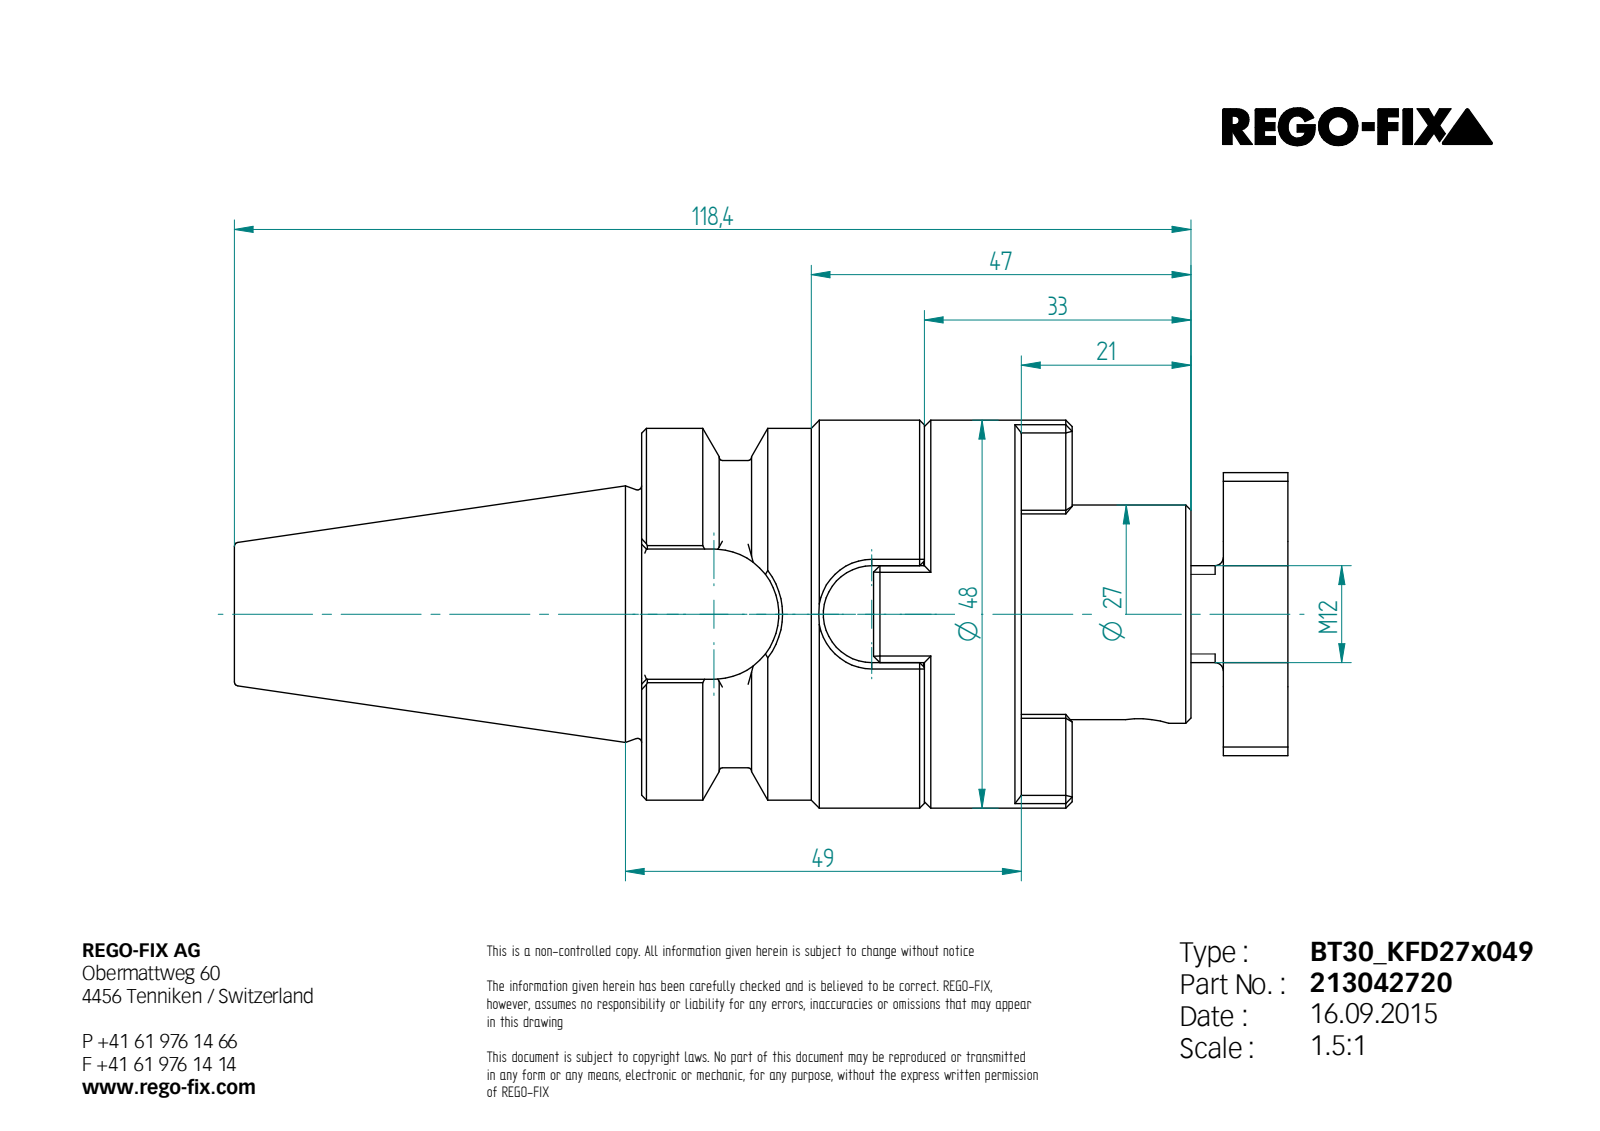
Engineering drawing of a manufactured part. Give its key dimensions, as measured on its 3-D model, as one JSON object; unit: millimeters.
{"step_written_by": "Unknown (AUTOMOTIVE_DESIGN)", "units": "millimeters", "bodies": {"solids": 3, "faces": 214, "planar": 119, "cylindrical": 39, "other": 56}, "overall_size": [130.4, 48, 48], "volume_mm3": 110950, "surface_area_mm2": 28862, "round_holes": [[10.11, 1], [12.5, 1], [13, 1], [27, 1]], "round_bosses_or_shafts": [[48, 1], [46, 1], [26.4, 1], [12, 1]], "partial_cylinders_radius": [[0.5, 8], [3, 4], [3.5, 2], [6, 1], [8.05, 1], [17.5, 1], [19, 1]], "face_to_face_distances": [12, 33, 8, 45, 35, 47, 80, 72, 37, 25]}
